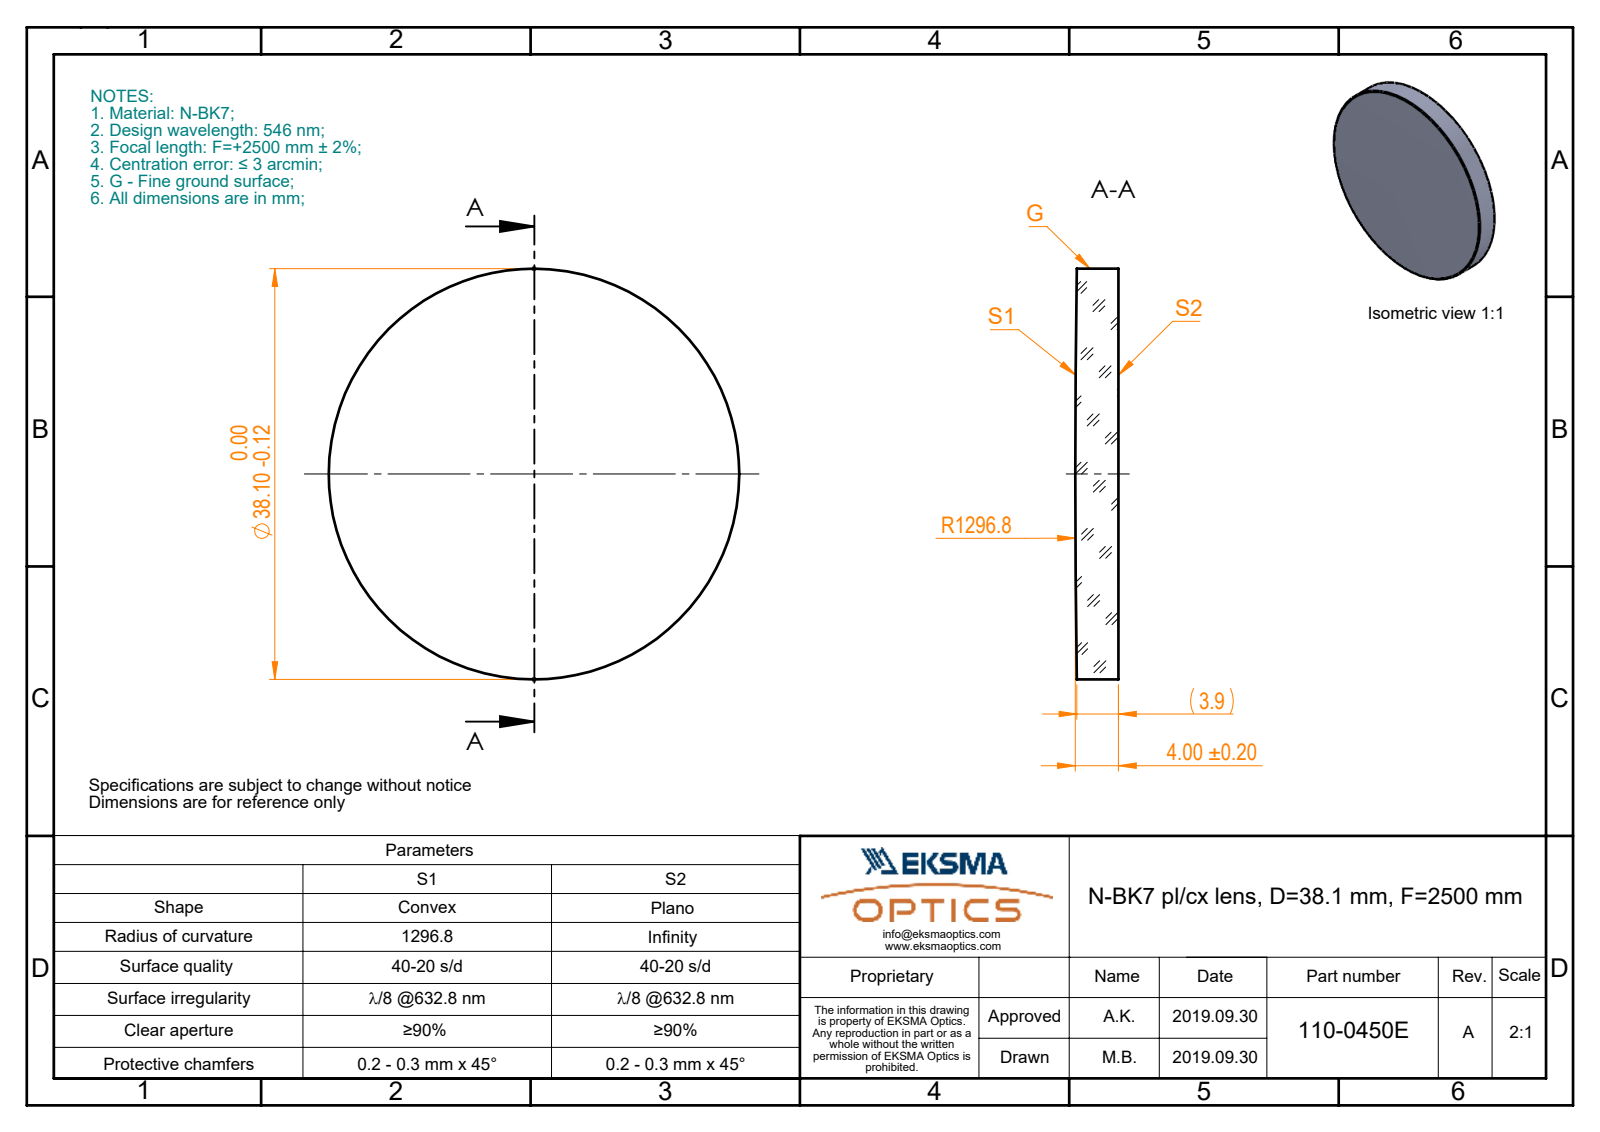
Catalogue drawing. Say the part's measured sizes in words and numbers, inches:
The part is named "110-0450E BK7 pl-cx 38.1 F2500". Its 3-D file was written by "SolidWorks 2019 (CONFIG_CONTROL_DESIGN)". It is 1 solid with 4 faces: 1 planar, 2 cylindrical and 1 other. Overall it measures 1.5 by 1.5 by 0.157 inches. Its volume is 0.273 cubic inches and its surface area 4.25 square inches. Round bosses or shafts: 1 of diameter 1.5.
